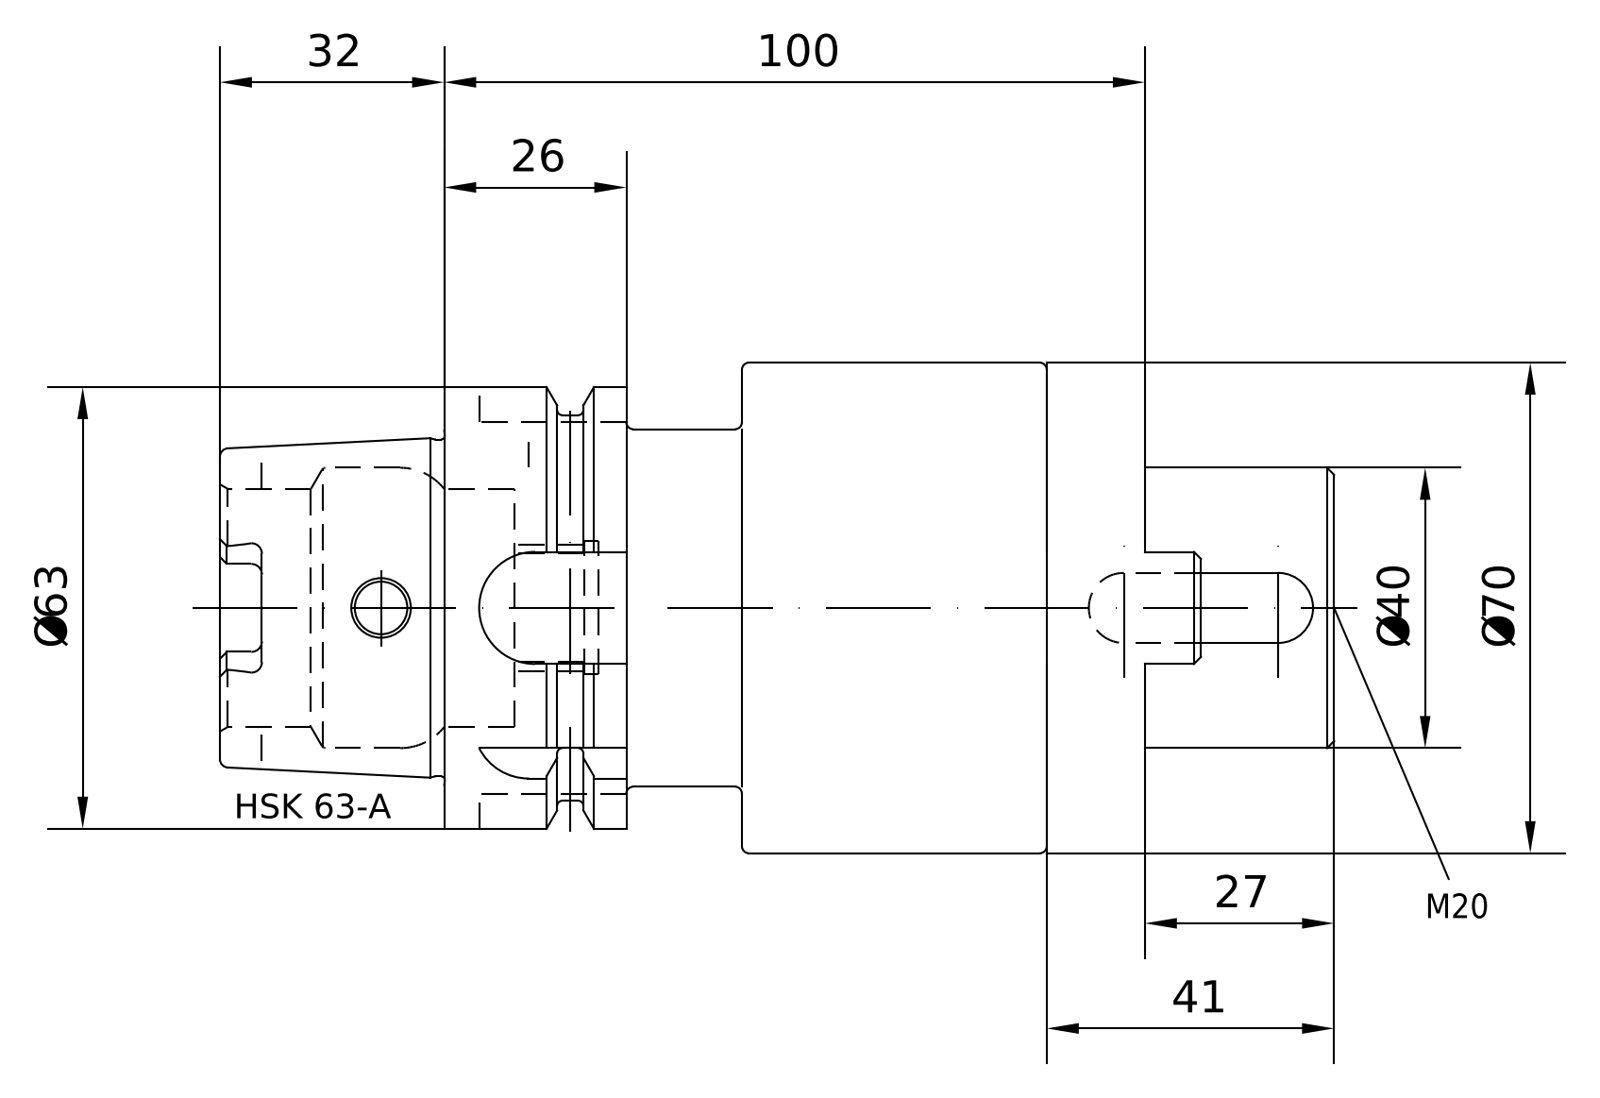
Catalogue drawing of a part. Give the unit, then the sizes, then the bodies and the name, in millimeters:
Units: millimetres
Overall size (bounding box): 159 × 70 × 70
Round holes (diameter × count): ⌀7.5 ×1, ⌀10 ×1, ⌀16.92 ×1, ⌀17.5 ×1, ⌀18.32 ×1, ⌀18.66 ×1, ⌀20 ×1, ⌀34 ×1, ⌀40 ×1, ⌀40.39 ×1, ⌀45 ×1
Round bosses / shafts (diameter × count): ⌀70 ×1, ⌀63 ×1, ⌀55 ×1, ⌀51 ×1, ⌀48.04 ×1, ⌀18 ×1
Partial cylindrical surfaces — rounded edges, fillets, slot ends (radius × count): R1.5 ×6, R3 ×4, R5 ×2, R8 ×1, R8.02 ×1, R8.05 ×1, R9.02 ×1
Main face-to-face distances: 14, 43.5, 57.5, 42.5, 86, 100, 127, 84.5, 41, 27
Volume: 353 786 mm³ · Surface area: 60 958 mm²
Bodies: 2 solids, 273 faces (125 planar, 66 cylindrical, 82 other)
Part name (STEP PRODUCT): A63-041-40; 85-200-40; A63-041-40_ASM
STEP written by: PRO/ENGINEER BY PARAMETRIC TECHNOLOGY CORPORATION, 2010430 (CONFIG_CONTROL_DESIGN)
